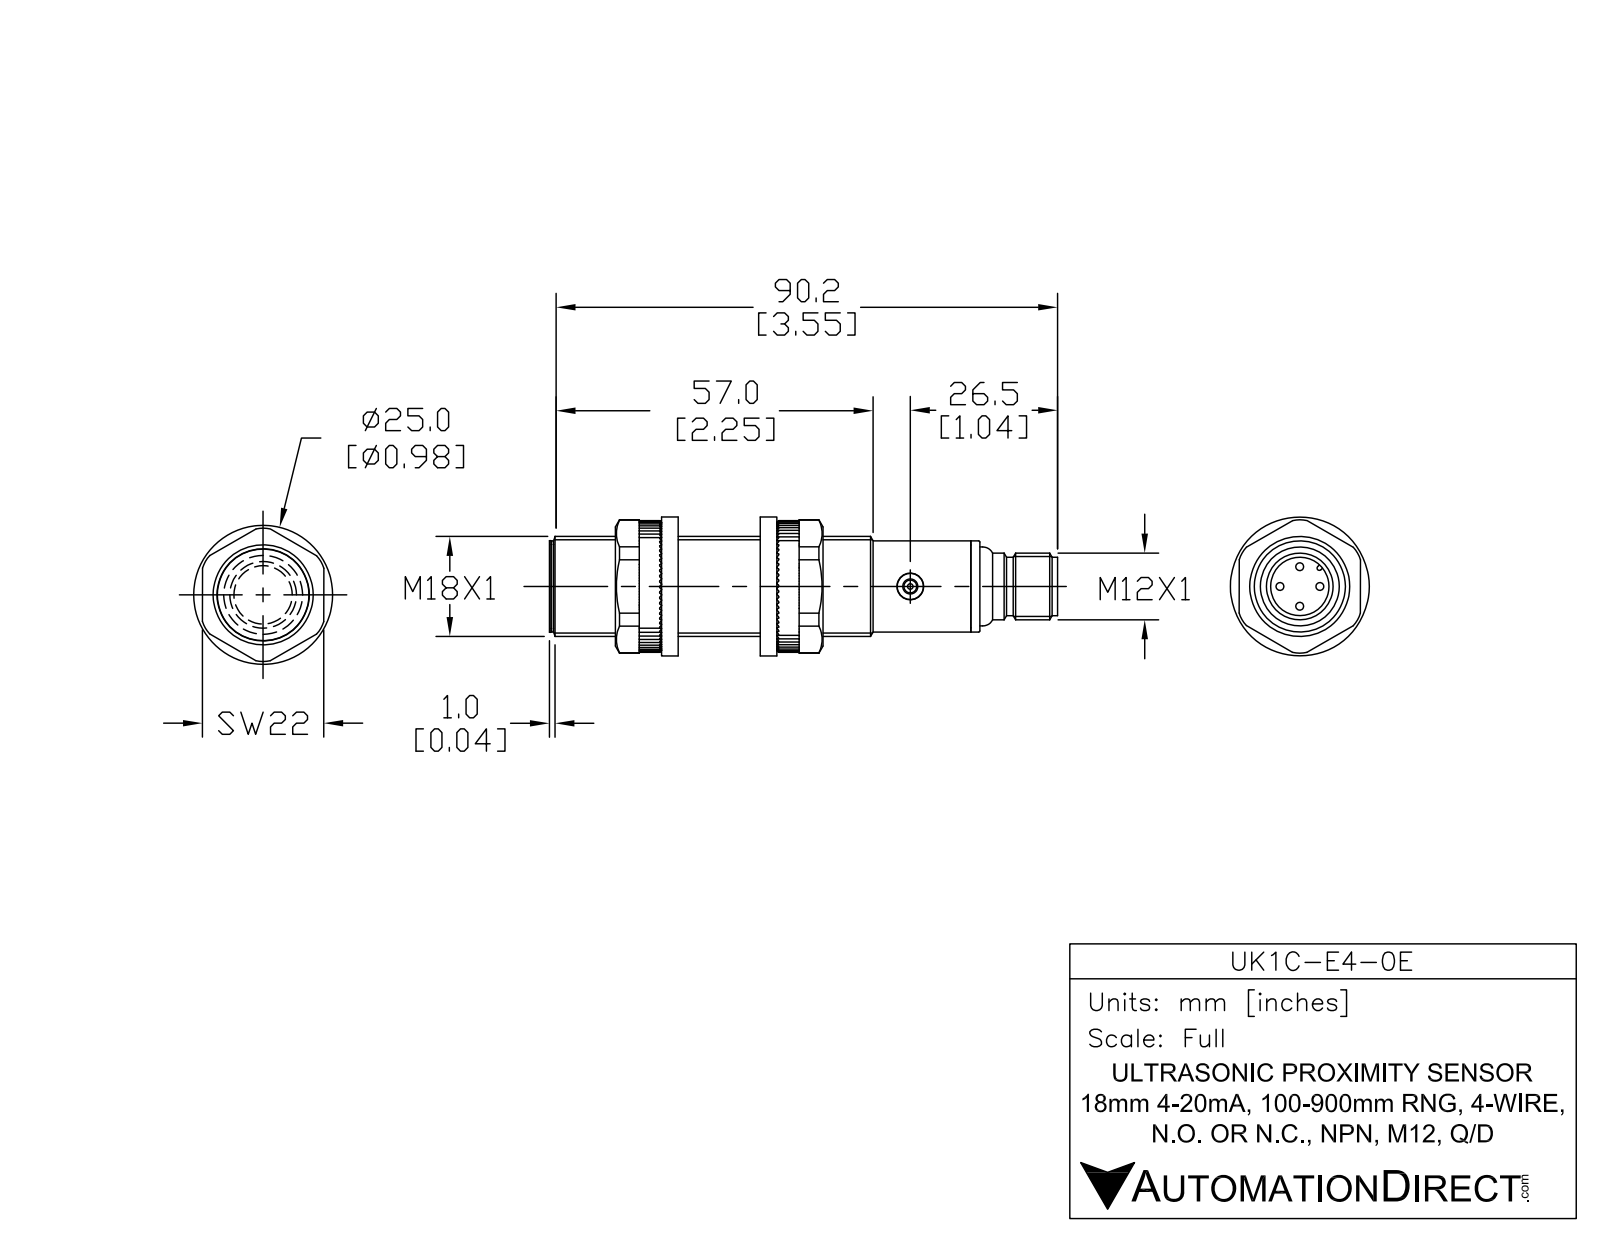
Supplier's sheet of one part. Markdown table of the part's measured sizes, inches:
| quantity | value |
| --- | --- |
| part name | UK1C-E4-0E |
| STEP written by | SolidWorks 2017 (AUTOMOTIVE_DESIGN) |
| units | inches |
| bodies | 6 solids, 106 faces (21 planar, 48 cylindrical, 37 other) |
| overall size | 3.606 × 0.709 × 0.709 |
| volume | 1.202 in³ |
| surface area | 10.68 in² |
| round holes (diameter × count) | 0.106 × 1, 0.185 × 1, 0.276 × 1, 0.327 × 1, 0.374 × 1 |
| round bosses / shafts (diameter × count) | 0.039 × 4, 0.709 × 1, 0.654 × 1, 0.646 × 1, 0.622 × 1, 0.559 × 1, 0.472 × 1, 0.413 × 1 |
| partial cylindrical surfaces (radius × count) | 0.024 × 1 |
| main face-to-face distances | 2.957, 0.039, 2.996, 0.037, 2.994, 0.043, 0.157, 3.055, 3.053, 3.016 |
